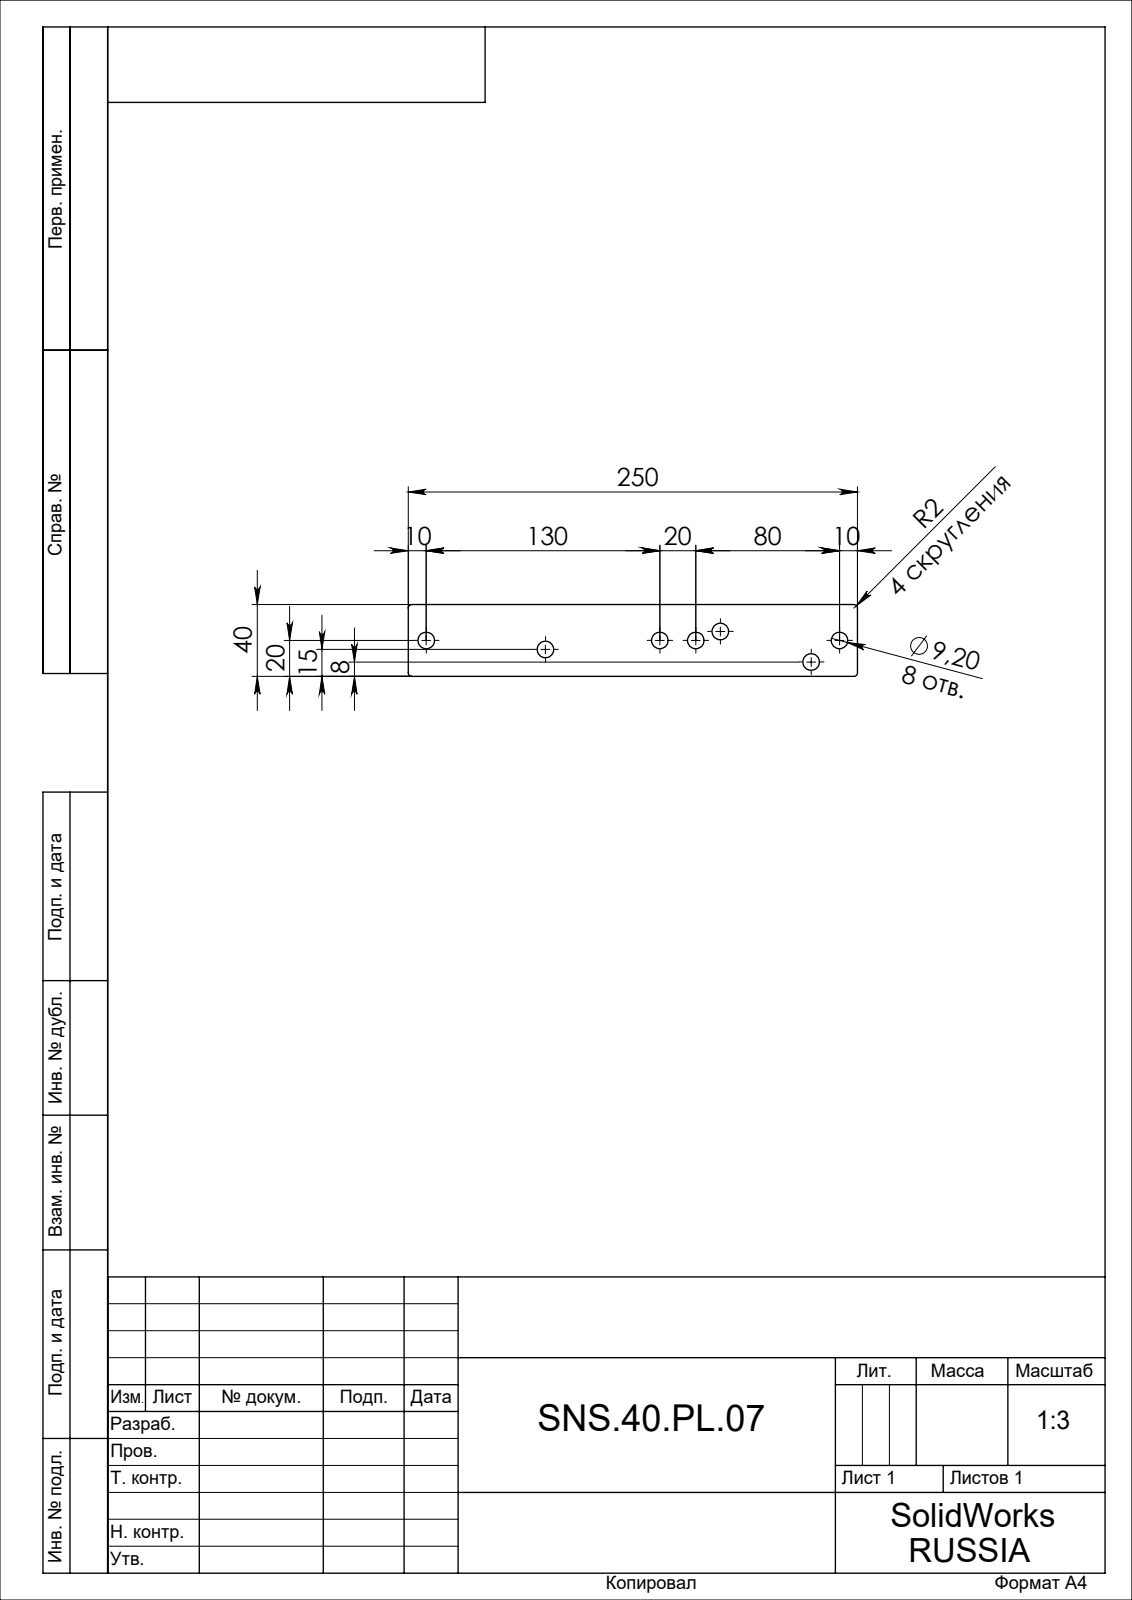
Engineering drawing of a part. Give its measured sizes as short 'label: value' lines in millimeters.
written by: SolidWorks 2018 (AUTOMOTIVE_DESIGN)
unit: mm
bodies: 1 solid, 24 faces (6 planar, 18 cylindrical, 0 other)
size: 250 × 40 × 3
volume: 28 594 mm³; area: 21 399 mm²
holes: 7× ⌀9.2
rounds: 4× R2
face distances: 3, 40, 250
hole spacings: 66.53, 163.74, 14.55, 19.82, 20, 34.03, 53.34, 63.86
